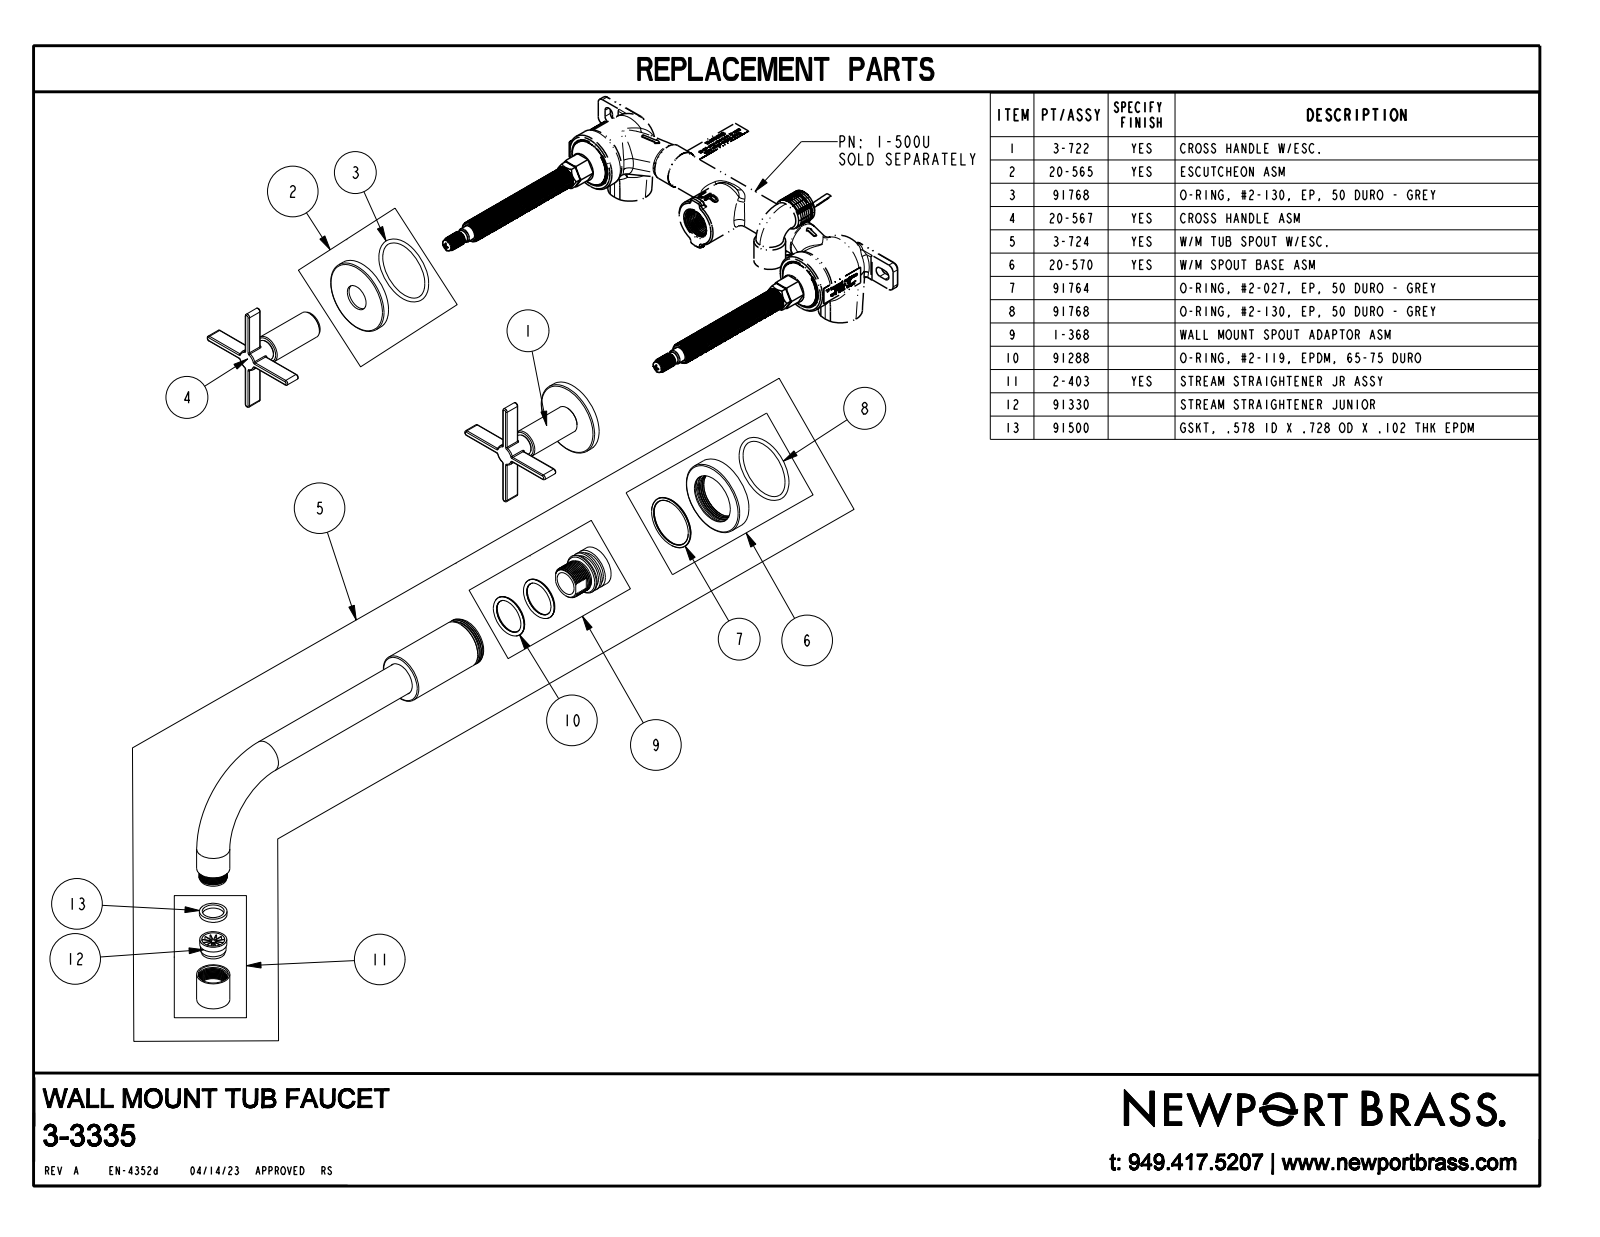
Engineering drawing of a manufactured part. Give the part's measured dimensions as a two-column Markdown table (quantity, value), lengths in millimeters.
| quantity | value |
| --- | --- |
| part name | 13532; 20-565_ASM; 13533; 13535 (+8 more) |
| STEP written by | CREO PARAMETRIC BY PTC INC, 2018400 (CONFIG_CONTROL_DESIGN) |
| units | millimeters |
| bodies | 11 solids, 718 faces (202 planar, 329 cylindrical, 187 other) |
| overall size | 277.9 × 276.2 × 220.6 |
| volume | 98 910 mm³ |
| surface area | 82 450 mm² |
| round holes (diameter × count) | 40.6 × 3, 2.8 × 2, 9.1 × 2, 10.1 × 2, 10.2 × 2, 13.1 × 2, 13.6 × 2, 15.2 × 2, 17.8 × 2, 19.1 × 2, 48 × 2, 3 × 1 |
| round bosses / shafts (diameter × count) | 17.3 × 3, 50.8 × 2, 41.9 × 2, 22.2 × 2, 19.1 × 2, 18.5 × 2, 14.3 × 2, 13 × 2 |
| partial cylindrical surfaces (radius × count) | 0.8 × 28, 1.9 × 8, 3.5 × 2, 7.6 × 1 |
| main face-to-face distances | 1.3, 3.8, 7.5, 1.8, 3, 5.7, 4.4, 2, 5.1, 9.5 |
| hole center spacings | 182.2, 182.3, 200 |
